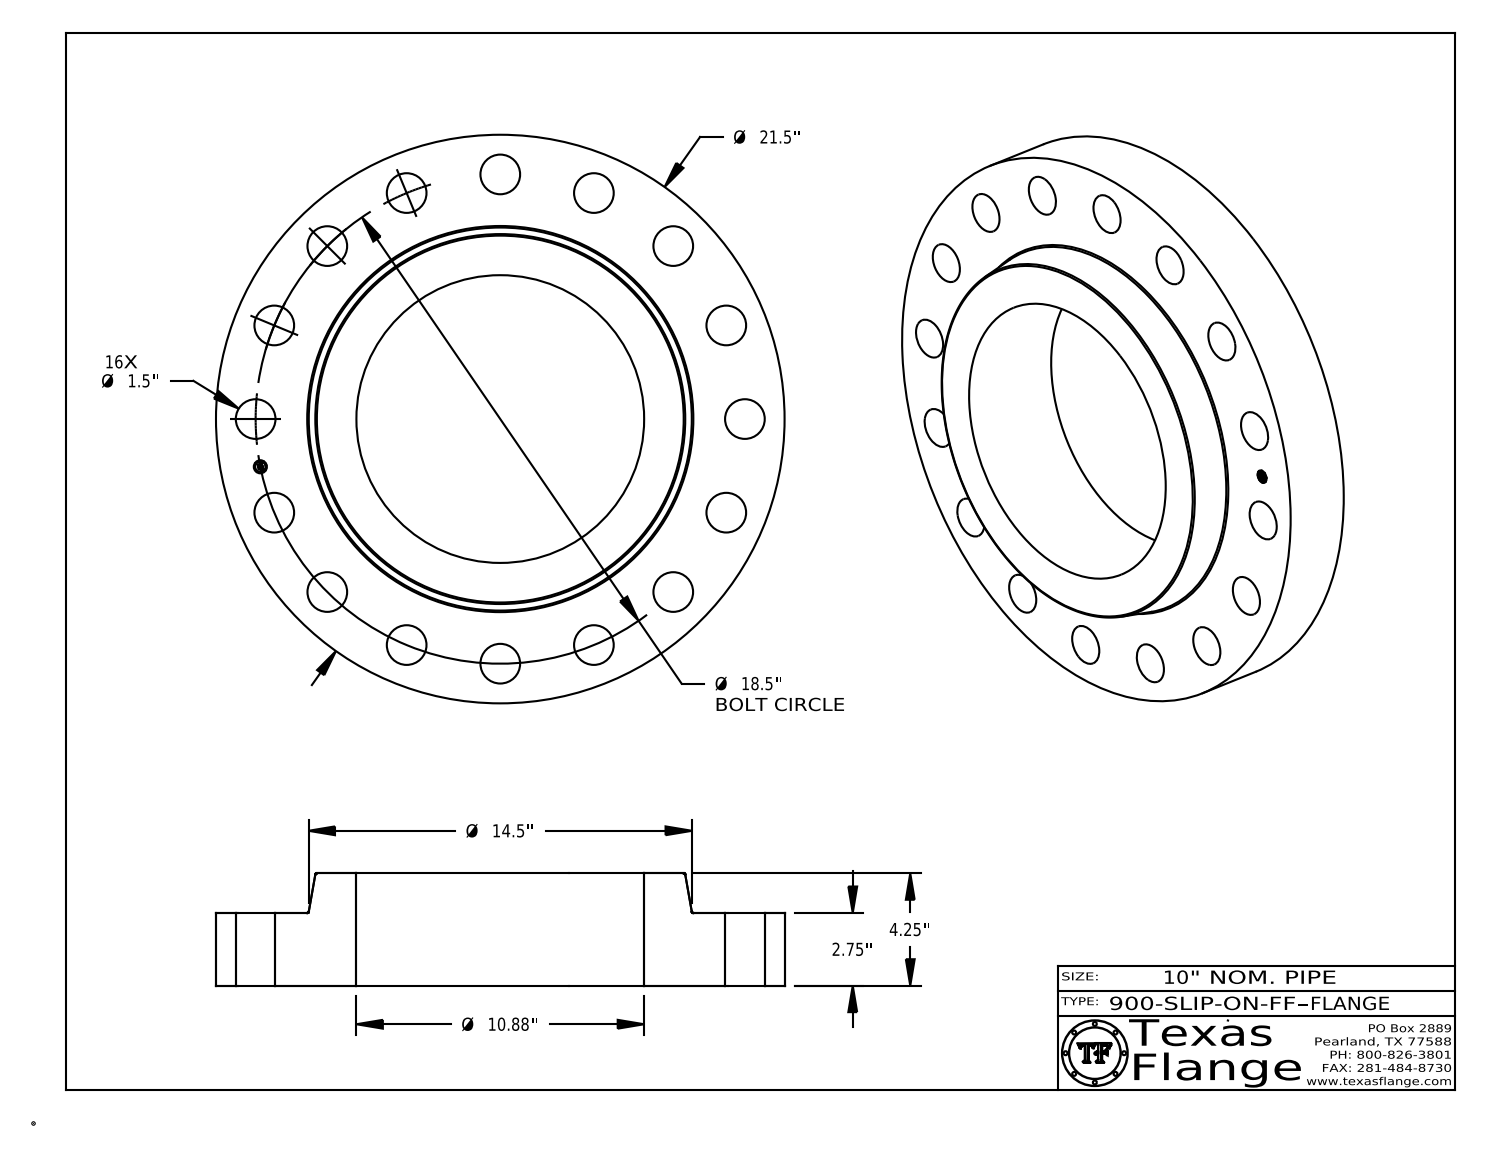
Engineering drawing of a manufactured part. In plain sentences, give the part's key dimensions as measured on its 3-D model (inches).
The part is named "900-SLIP-ON-FF". Its 3-D file was written by "CATIA V5 STEP AP214 (AUTOMOTIVE_DESIGN)". It is 1 solid with 430 faces: 368 planar, 56 cylindrical and 6 other. Overall it measures 21.5 by 21.5 by 4.25 inches. Its volume is 764.3 cubic inches and its surface area 1 077 square inches. Round holes: 16 of diameter 1.5, 1 of diameter 0.495, 1 of diameter 10.88. Round bosses or shafts: 8 of diameter 0.03, 1 of diameter 21.5, 1 of diameter 0.39. The main face-to-face distances are 2.75, 4.25, 1.5, 2.735, 0.015, 1.515, 0.148, 0.145, 0.027, 0.096. The hole center spacings are 15.382, 7.08, 9.25, 13.081, 3.609, 3.609, 10.278, 10.278.
